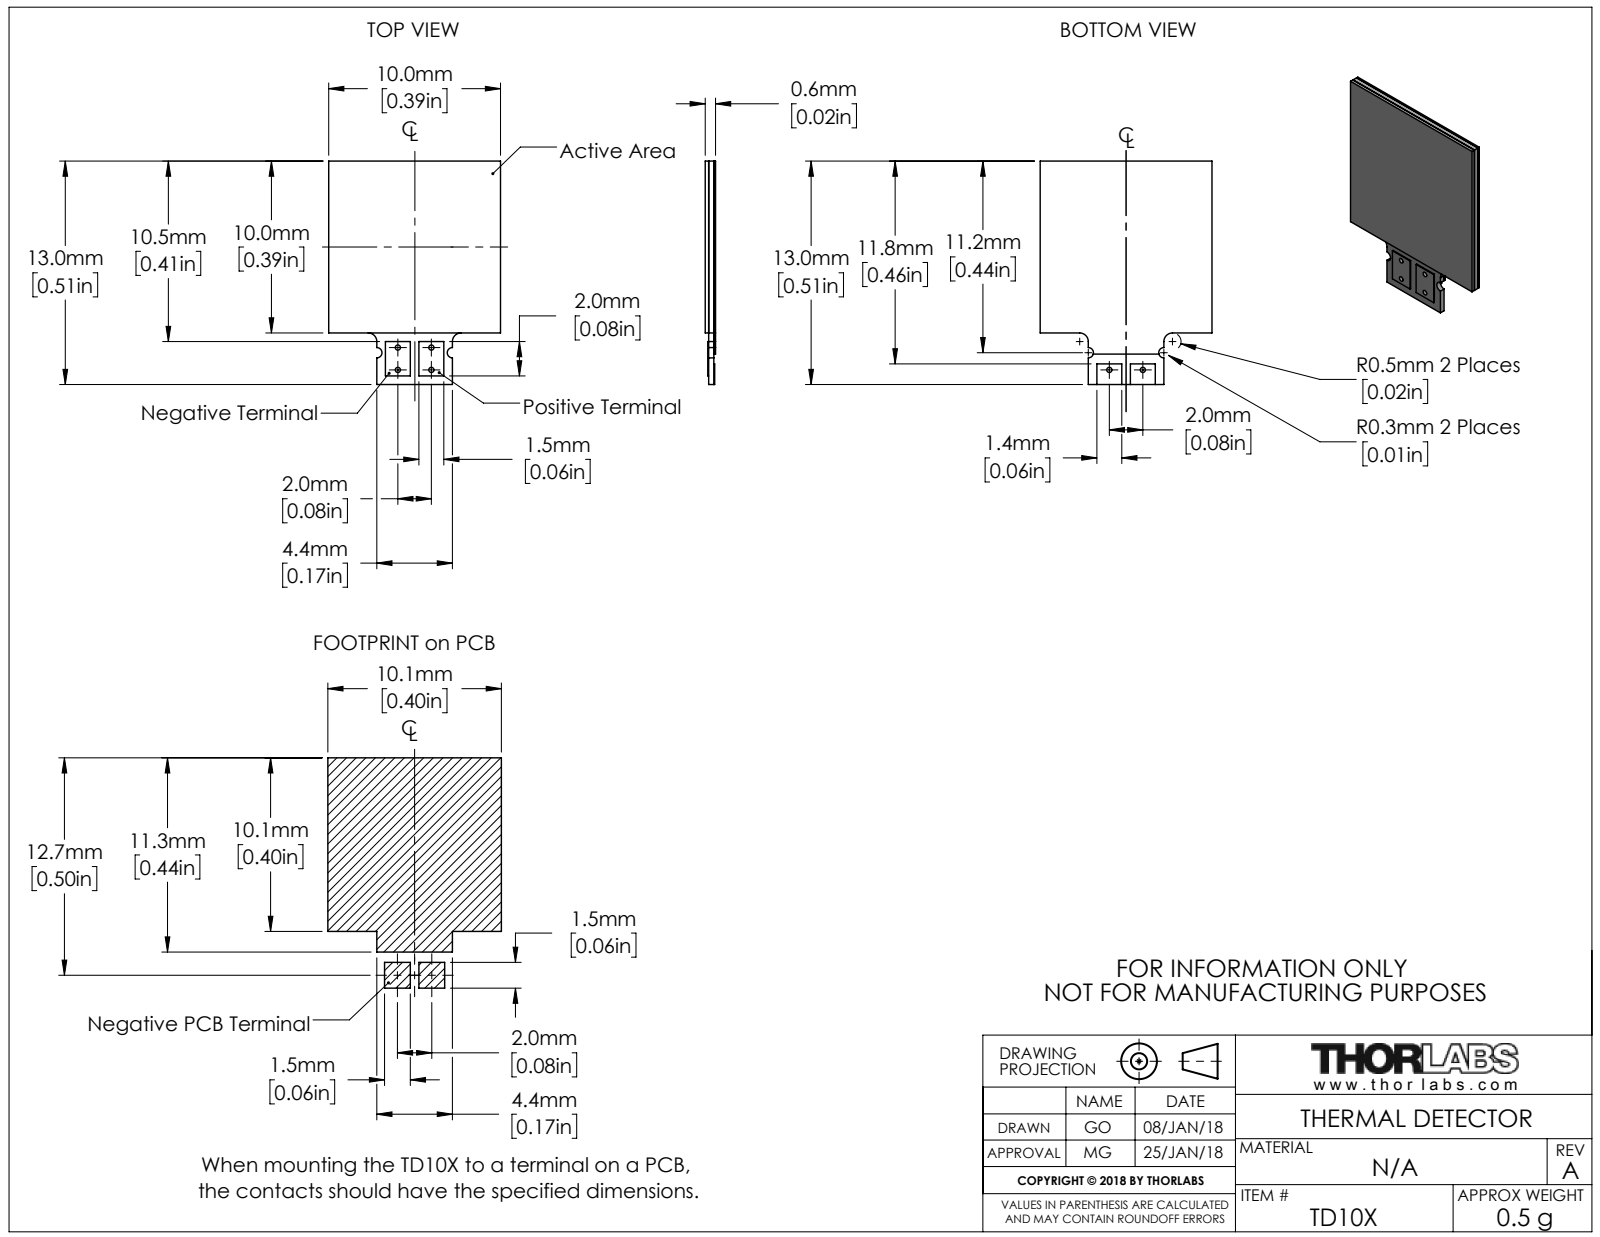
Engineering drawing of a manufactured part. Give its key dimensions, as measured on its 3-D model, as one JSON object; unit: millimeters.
{"part_name": "MTN10557-E0W", "step_written_by": "SolidWorks 2016 (CONFIG_CONTROL_DESIGN)", "units": "millimeters", "bodies": {"solids": 3, "faces": 64, "planar": 46, "cylindrical": 18, "other": 0}, "overall_size": [13, 10, 0.6], "volume_mm3": 65, "surface_area_mm2": 665, "round_holes": [[0.3, 4]], "partial_cylinders_radius": [[0.3, 2], [0.5, 2]], "face_to_face_distances": [0.4, 0.5, 0.6, 10, 0.35, 0.45, 0.55, 3, 13, 2.8], "hole_center_spacings": [1.3, 1.95, 2.34]}
